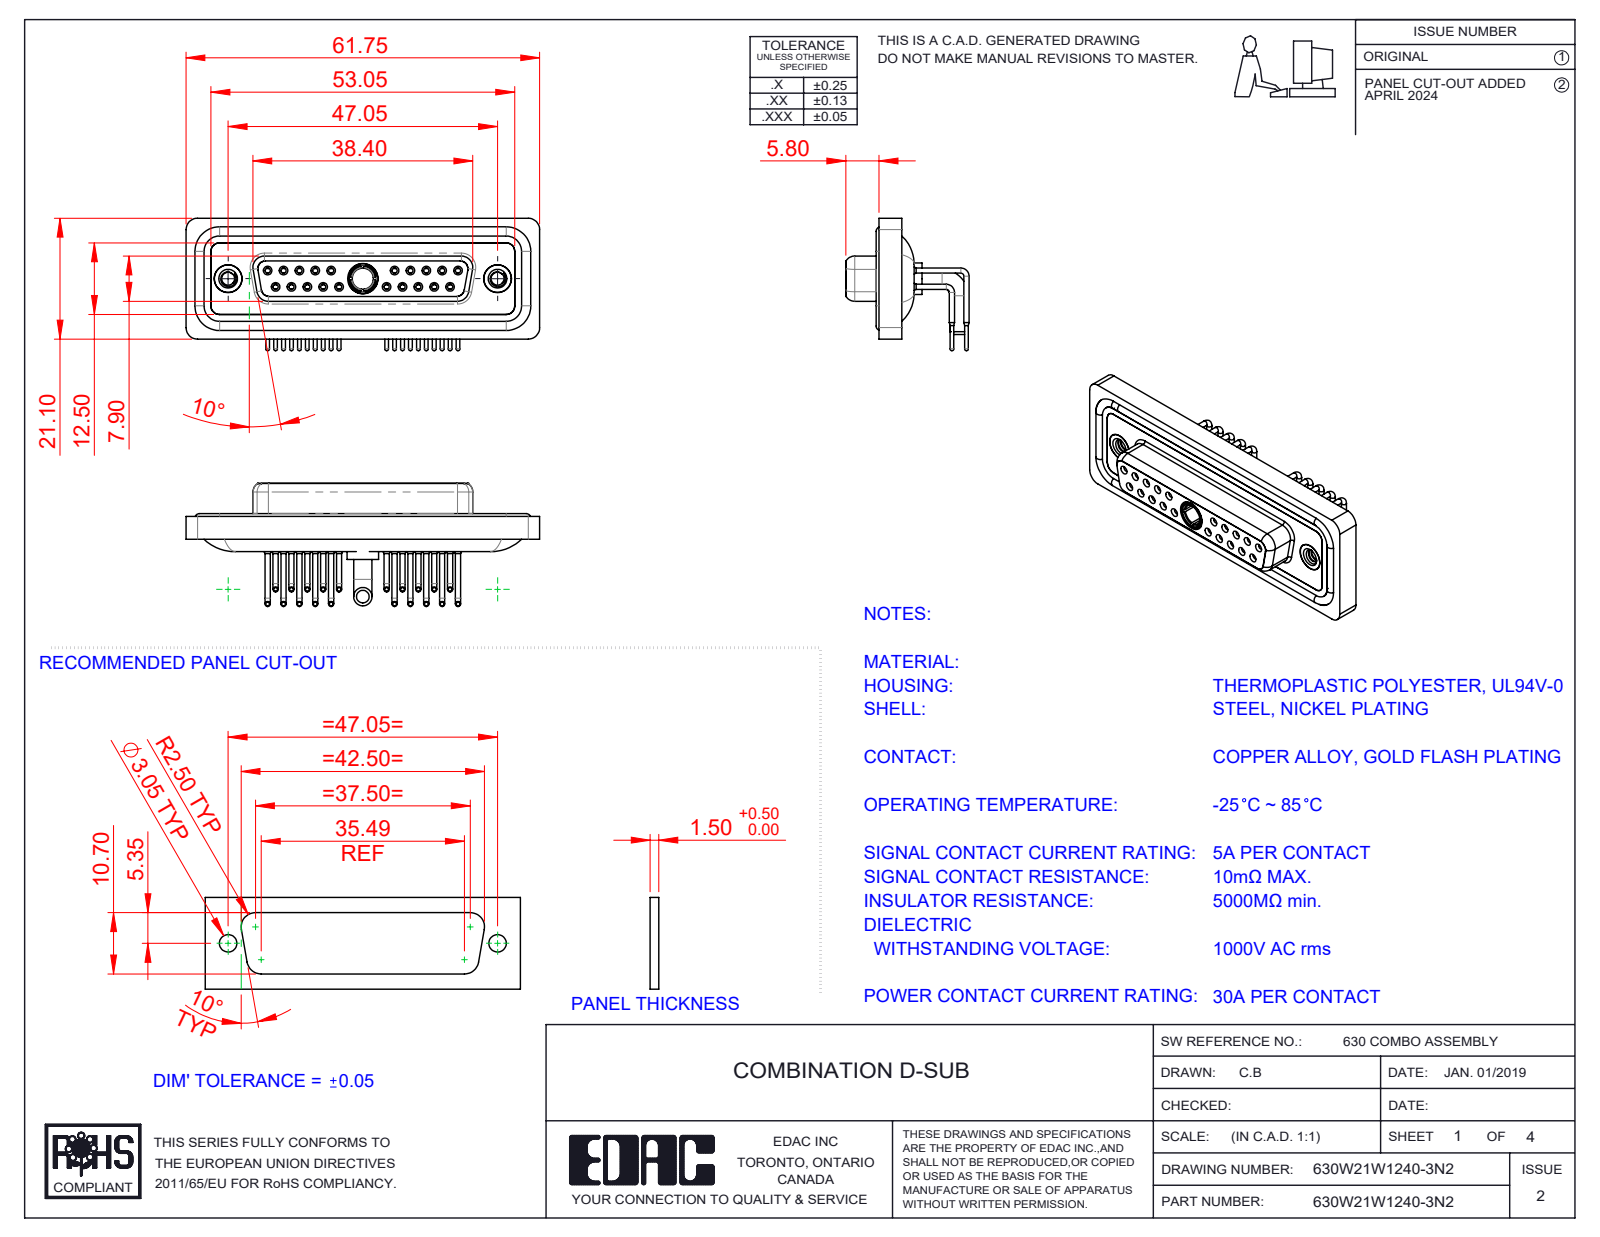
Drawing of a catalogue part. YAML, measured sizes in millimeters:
part_name: "630Combo Waterproof Housing_25 Contacts; 630Combo Housing_21W1; 630Combo Contact Row 1_50 Contacts; 630Combo Shell Front_25 Contacts (+5 more)"
step_written_by: "SolidWorks 2023 (CONFIG_CONTROL_DESIGN)"
units: millimeters
bodies: {solids: 29, faces: 1524, planar: 434, cylindrical: 673, other: 417}
overall_size: [61.75, 23.12, 21.53]
volume: 8533
surface_area: 14798
round_holes:
  - {diameter: 0.9, count: 20}
  - {diameter: 1.1, count: 20}
  - {diameter: 1.5, count: 20}
  - {diameter: 2, count: 20}
  - {diameter: 1.6, count: 10}
  - {diameter: 1.7, count: 10}
  - {diameter: 4.85, count: 3}
  - {diameter: 2.26, count: 2}
  - {diameter: 4, count: 2}
  - {diameter: 4.05, count: 2}
  - {diameter: 5, count: 2}
  - {diameter: 3.7, count: 1}
round_bosses_or_shafts:
  - {diameter: 0.9, count: 20}
  - {diameter: 0.65, count: 20}
  - {diameter: 1.6, count: 14}
  - {diameter: 4.95, count: 2}
  - {diameter: 4.8, count: 2}
  - {diameter: 3.2, count: 2}
  - {diameter: 5.5, count: 1}
  - {diameter: 5.2, count: 1}
partial_cylinders:
  - {radius: 1.5, count: 18}
  - {radius: 2, count: 18}
  - {radius: 1.35, count: 8}
  - {radius: 1.6, count: 8}
  - {radius: 0.25, count: 4}
  - {radius: 0.5, count: 4}
  - {radius: 0.6, count: 4}
  - {radius: 0.65, count: 4}
face_to_face_distances: [0.4, 1.8, 4.1, 1.6, 1.1, 2.5, 3.1, 1.5, 9.8, 0.45]
hole_center_spacings: [3.16, 2.77, 5.54, 8.31, 5.04, 19.39, 20.97, 22.16]
